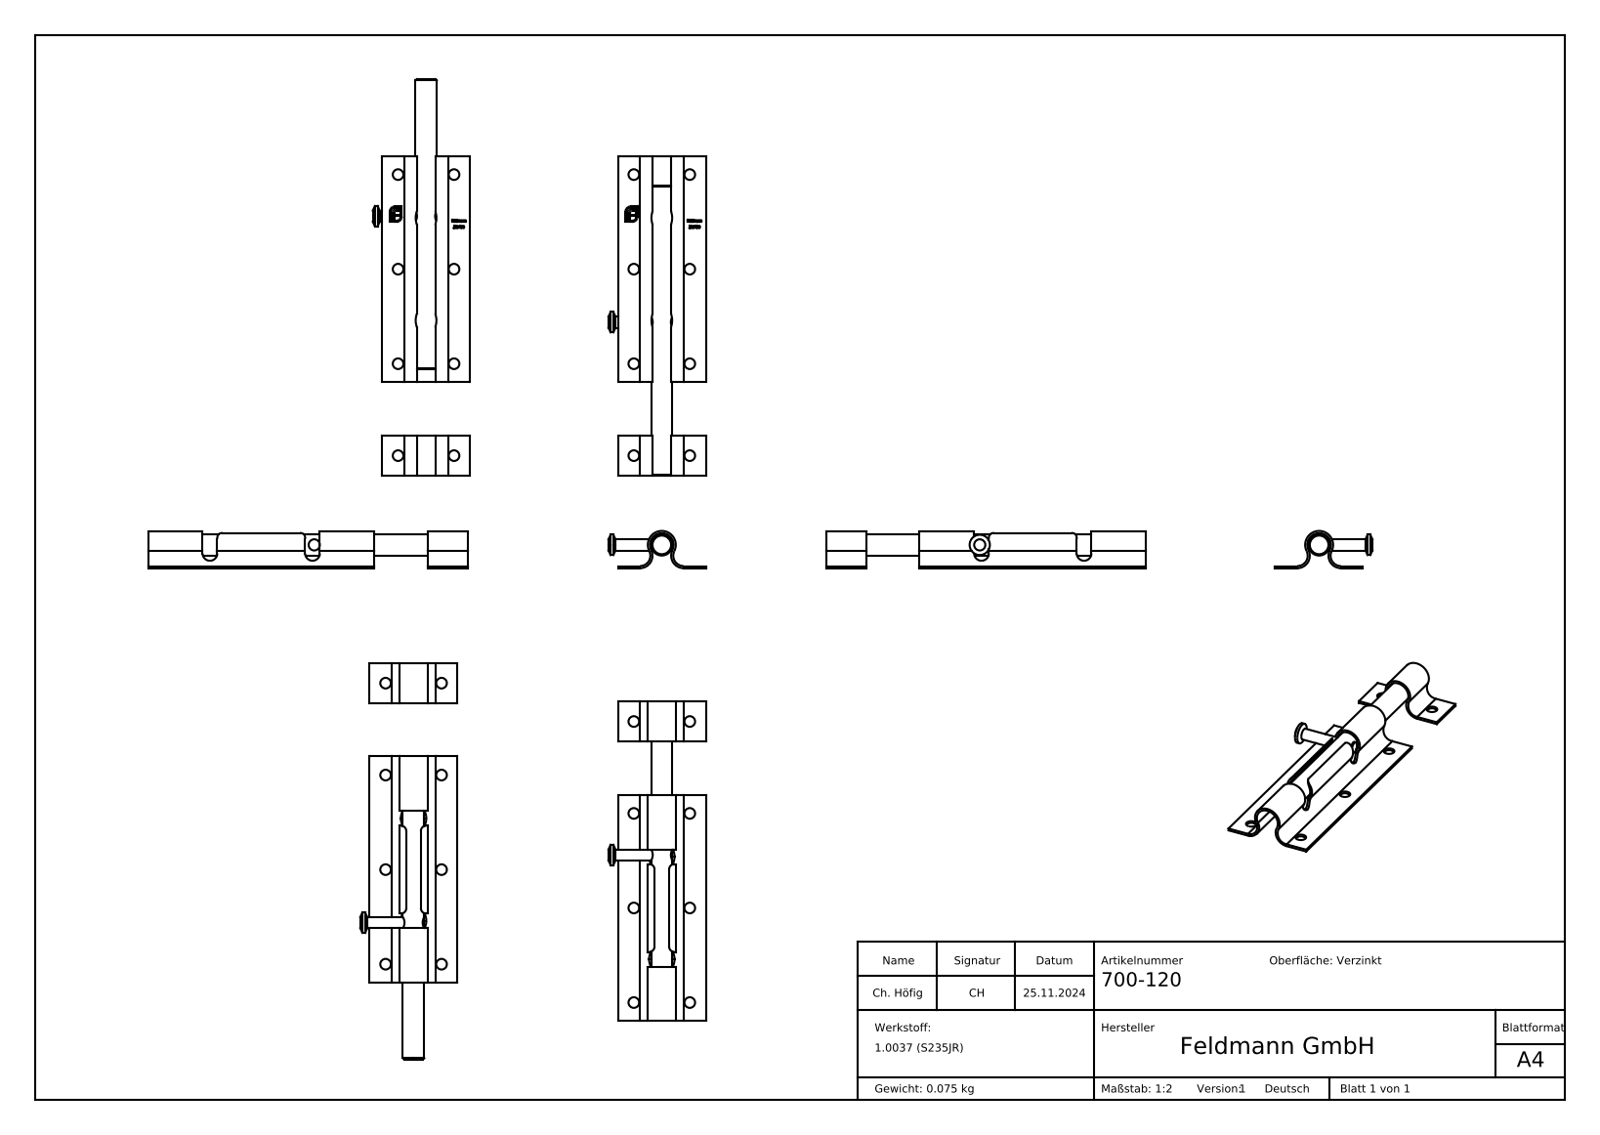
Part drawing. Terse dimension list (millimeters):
name: 700-XXX Teil1_700-120 Teil1; 700-XXX Teil3_700-XXX Teil3; 700-XXX Teil2_700-120 Teil2; 700-120
written by: SolidWorks 2018 (CONFIG_CONTROL_DESIGN)
unit: mm
bodies: 4 solids, 293 faces (146 planar, 42 cylindrical, 105 other)
size: 120 × 36.5 × 14
volume: 9 581 mm³; area: 13 443 mm²
holes: 8× ⌀4, 1× ⌀4.2
bosses: 1× ⌀8, 1× ⌀7.6
rounds: 4× R2, 2× R2.75, 2× R3.89, 2× R4.69, 1× R4.45, 1× R5.25
face distances: 0.8, 33, 13.75, 19.25, 15, 20.5, 94, 120, 105, 35
hole spacings: 21, 35.5, 41.25, 34.5, 40.39, 70, 71, 73.08
